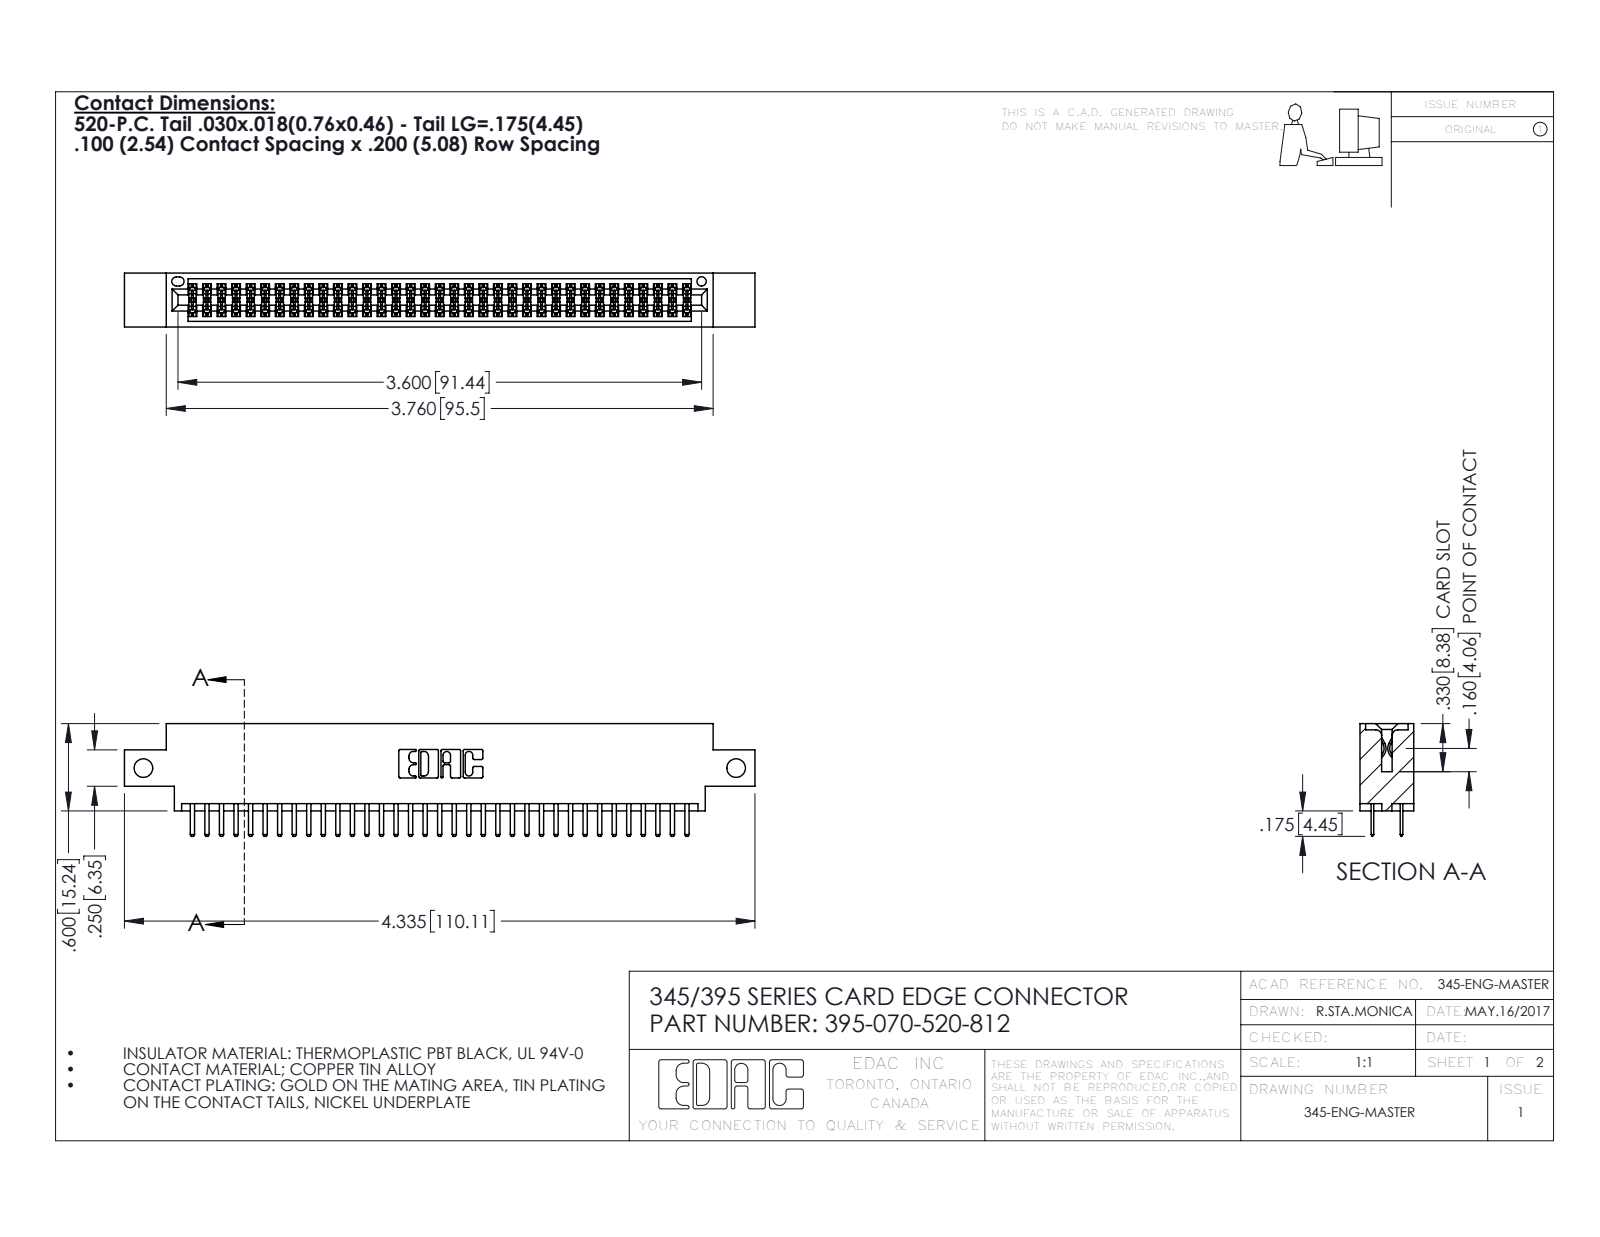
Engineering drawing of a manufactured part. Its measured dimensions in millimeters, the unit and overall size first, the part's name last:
Units: millimetres
Overall size (bounding box): 110.1 × 19.7 × 9.4
Round holes (diameter × count): ⌀3.3 ×2, ⌀1.6 ×1
Partial cylindrical surfaces — rounded edges, fillets, slot ends (radius × count): R0.2 ×105, R0.3 ×74, R0.3 ×22, R0.2 ×6, R0.8 ×6, R0.7 ×3, R0.4 ×2, R0.5 ×2
Main face-to-face distances: 7.6, 1.8, 5.1, 9.4, 2.5, 6.9, 0.6, 5.7, 0.6, 4.4
Hole centre spacings: 103.5
Volume: 10 400 mm³ · Surface area: 15 180 mm²
Bodies: 71 solids, 3910 faces (2534 planar, 1376 cylindrical, 0 other)
Part name (STEP PRODUCT): 345-292-001_345-293-120; 395-070-520-812; 345 Part_0.170 Offset - Side Mount
STEP written by: SolidWorks 2016 (CONFIG_CONTROL_DESIGN)
